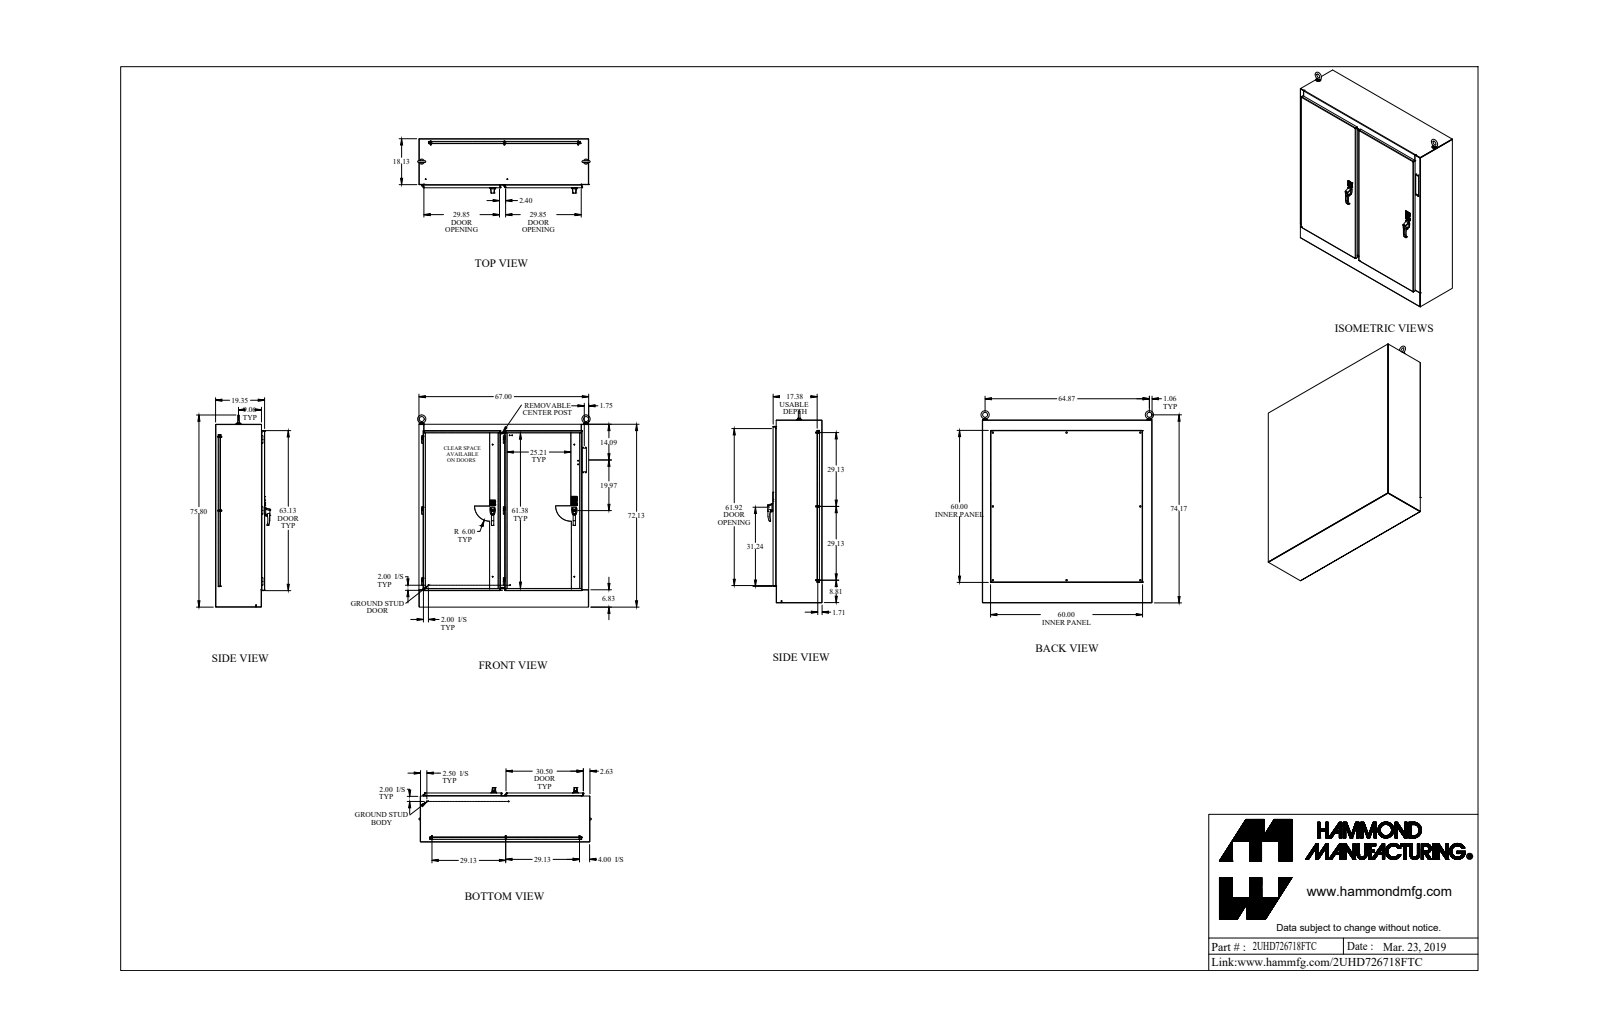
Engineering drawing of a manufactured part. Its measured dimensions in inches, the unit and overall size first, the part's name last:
Units: inches
Overall size (bounding box): 75.799 × 68.122 × 21.466
Round holes (diameter × count): ⌀0.196 ×12, ⌀0.281 ×11, ⌀0.307 ×11, ⌀0.25 ×8, ⌀0.35 ×8, ⌀0.313 ×6, ⌀0.445 ×5, ⌀0.255 ×4, ⌀0.257 ×4, ⌀0.282 ×4, ⌀0.375 ×4, ⌀0.39 ×4
Round bosses / shafts (diameter × count): ⌀0.25 ×19, ⌀1 ×12, ⌀0.65 ×9, ⌀0.375 ×9, ⌀0.33 ×9, ⌀0.281 ×8, ⌀0.75 ×6, ⌀0.625 ×6
Partial cylindrical surfaces — rounded edges, fillets, slot ends (radius × count): R0.125 ×56, R0.06 ×51, R0.5 ×38, R0.017 ×32, R0.185 ×30, R0.03 ×28, R0.032 ×12, R0.09 ×12
Main face-to-face distances: 0.125, 0.05, 17.431, 19.369, 19.243, 1.937, 1.812, 1.887, 1.762, 17.481
Hole centre spacings: 32.25, 1.126, 1.287, 32.269, 40.766, 1, 2, 24.937
Volume: 3 971 in³ · Surface area: 43 793 in²
Bodies: 214 solids, 3030 faces (1762 planar, 894 cylindrical, 374 other)
Part name (STEP PRODUCT): 2UHD726718FTC
STEP written by: SolidWorks 2018 (AUTOMOTIVE_DESIGN)
